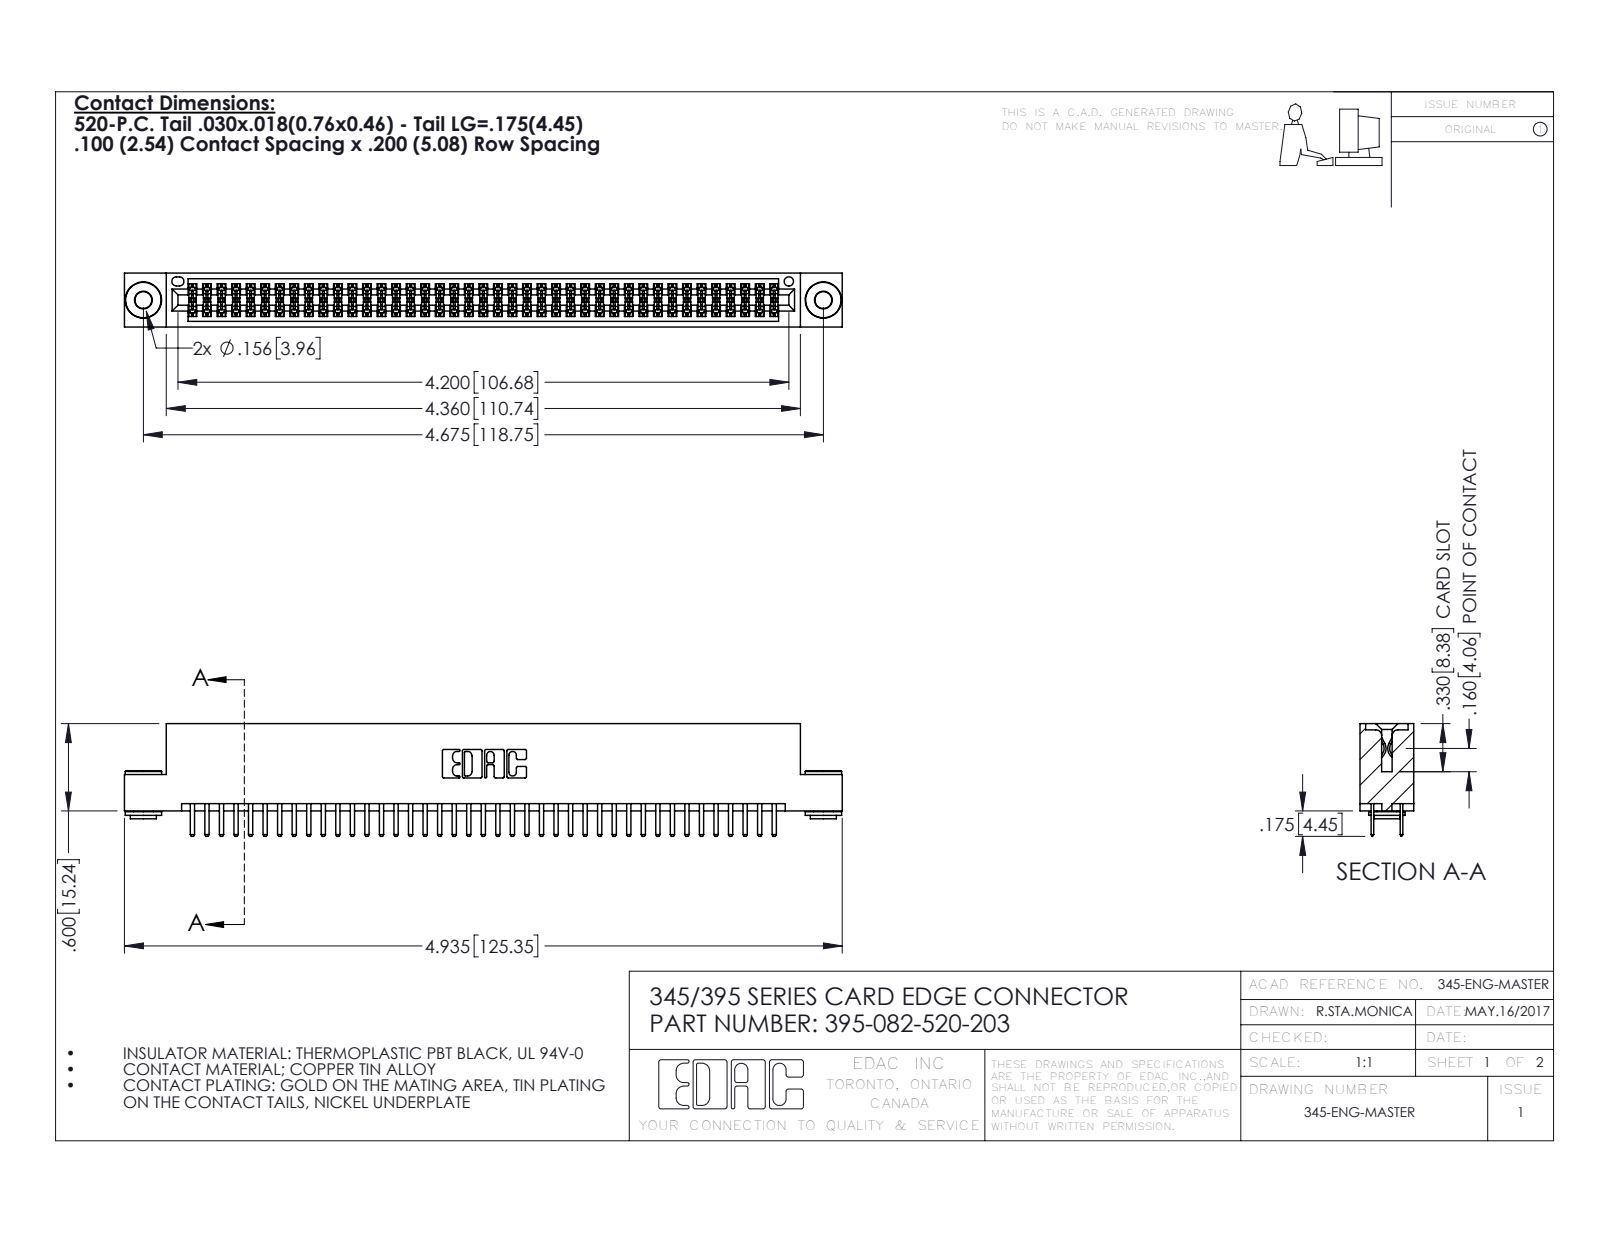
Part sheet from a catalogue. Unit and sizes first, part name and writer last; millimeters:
Units: millimetres
Overall size (bounding box): 125.3 × 19.7 × 9.4
Round holes (diameter × count): ⌀2.9 ×2, ⌀4 ×2, ⌀1.6 ×1
Round bosses / shafts (diameter × count): ⌀6.4 ×2, ⌀4.6 ×2, ⌀3.5 ×2
Partial cylindrical surfaces — rounded edges, fillets, slot ends (radius × count): R0.2 ×123, R0.3 ×86, R0.3 ×22, R0.2 ×6, R0.8 ×6, R0.7 ×3, R0.4 ×2, R0.5 ×2
Main face-to-face distances: 1.8, 7.6, 5.1, 9.4, 0.6, 2.5, 6.9, 5.7, 0.6, 1.8
Hole centre spacings: 6.9, 112.8, 118.7
Volume: 12 100 mm³ · Surface area: 18 070 mm²
Bodies: 85 solids, 4592 faces (2960 planar, 1624 cylindrical, 8 other)
Part name (STEP PRODUCT): 345-250-002_345-250-002-102; 345-292-001_345-293-120; 395-082-520-203; 345 Part_Flush Mounting Lugs - 0.156 Dia-TH
STEP written by: SolidWorks 2016 (CONFIG_CONTROL_DESIGN)
